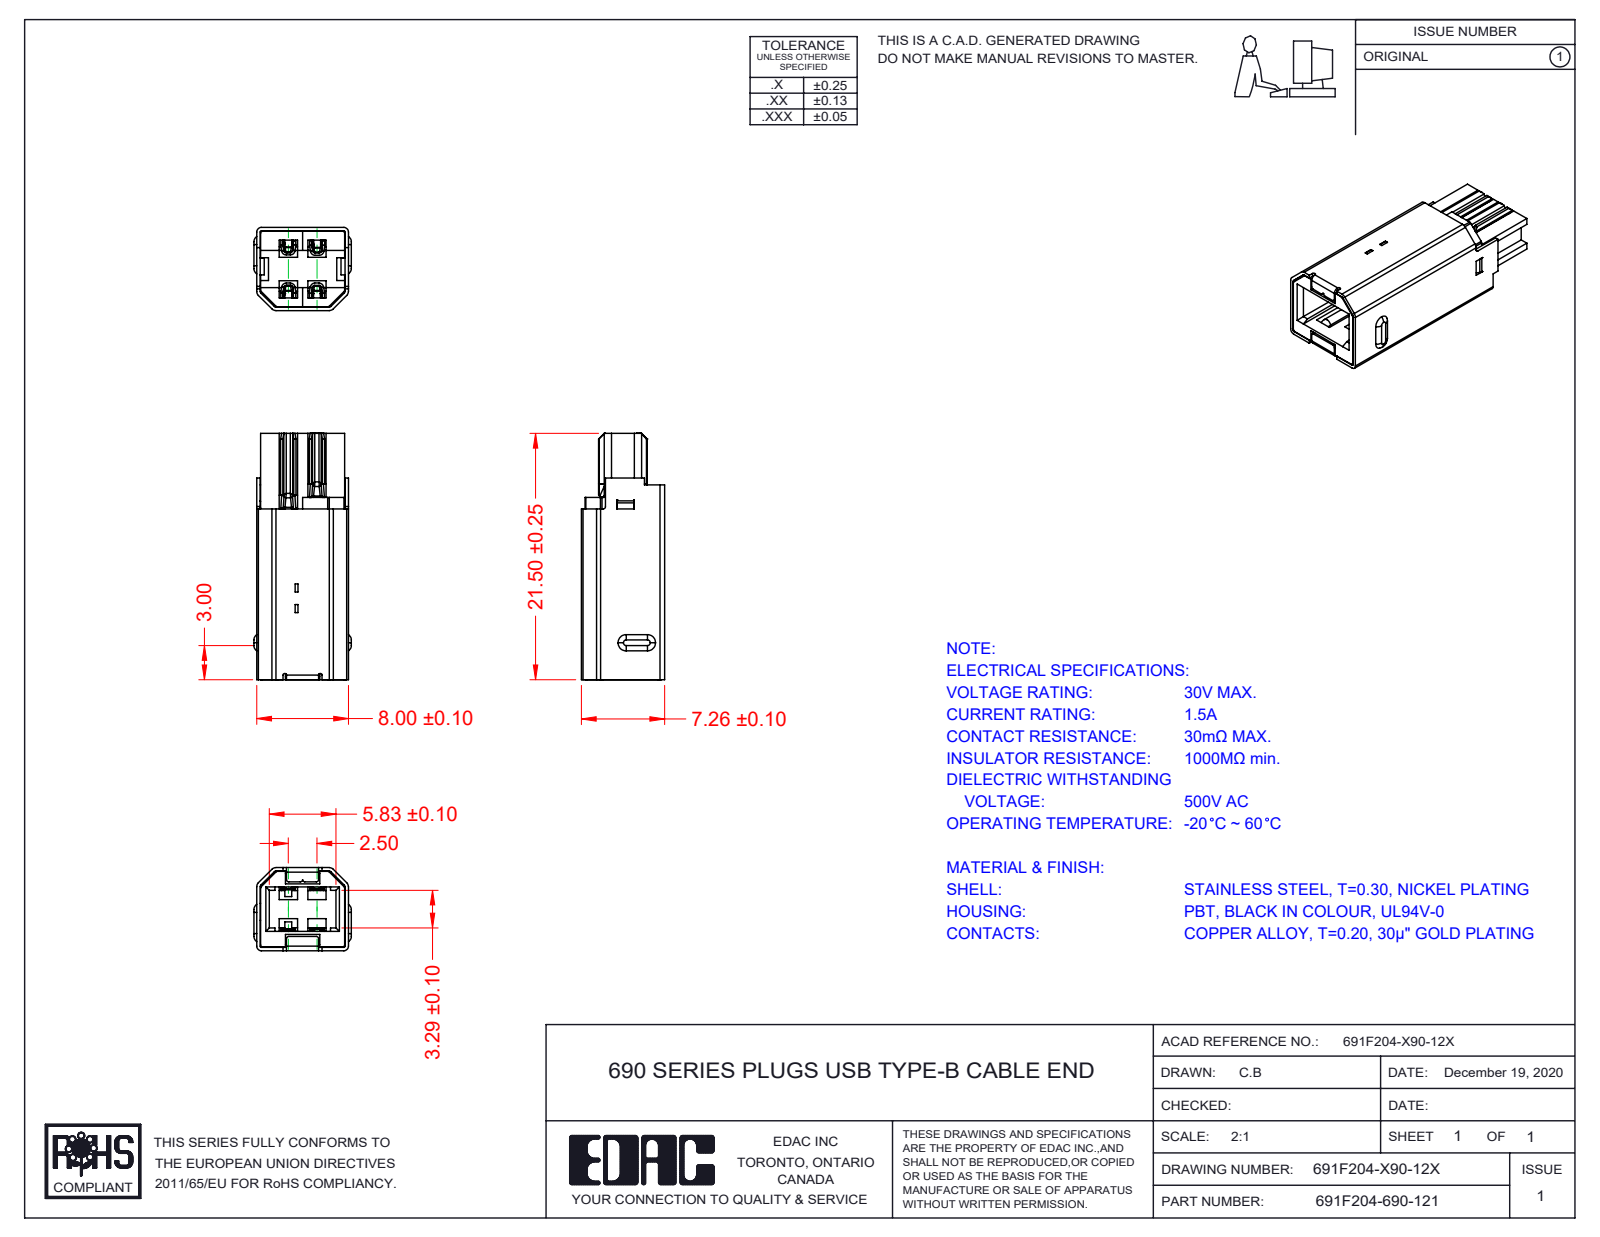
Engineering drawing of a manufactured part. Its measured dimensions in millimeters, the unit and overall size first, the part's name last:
Units: millimetres
Overall size (bounding box): 21.51 × 8.5 × 7.26
Partial cylindrical surfaces — rounded edges, fillets, slot ends (radius × count): R0.2 ×33, R0.4 ×12, R0.15 ×10, R0.35 ×8, R0.5 ×8, R0.1 ×4, R0.25 ×4, R0.28 ×4
Main face-to-face distances: 7.7, 0.32, 4.15, 6.96, 0.9, 3.25, 6.62, 6.92, 3.55, 0.34
Volume: 712 mm³ · Surface area: 2 334 mm²
Bodies: 6 solids, 865 faces (425 planar, 116 cylindrical, 324 other)
Part name (STEP PRODUCT): 691F204-190-121; Insulator 691F204-X90-12X_Black; Shell 691F204-X90-12X; Contact2 691F204-X90-12X (+1 more)
STEP written by: SolidWorks 2020 (AUTOMOTIVE_DESIGN)
